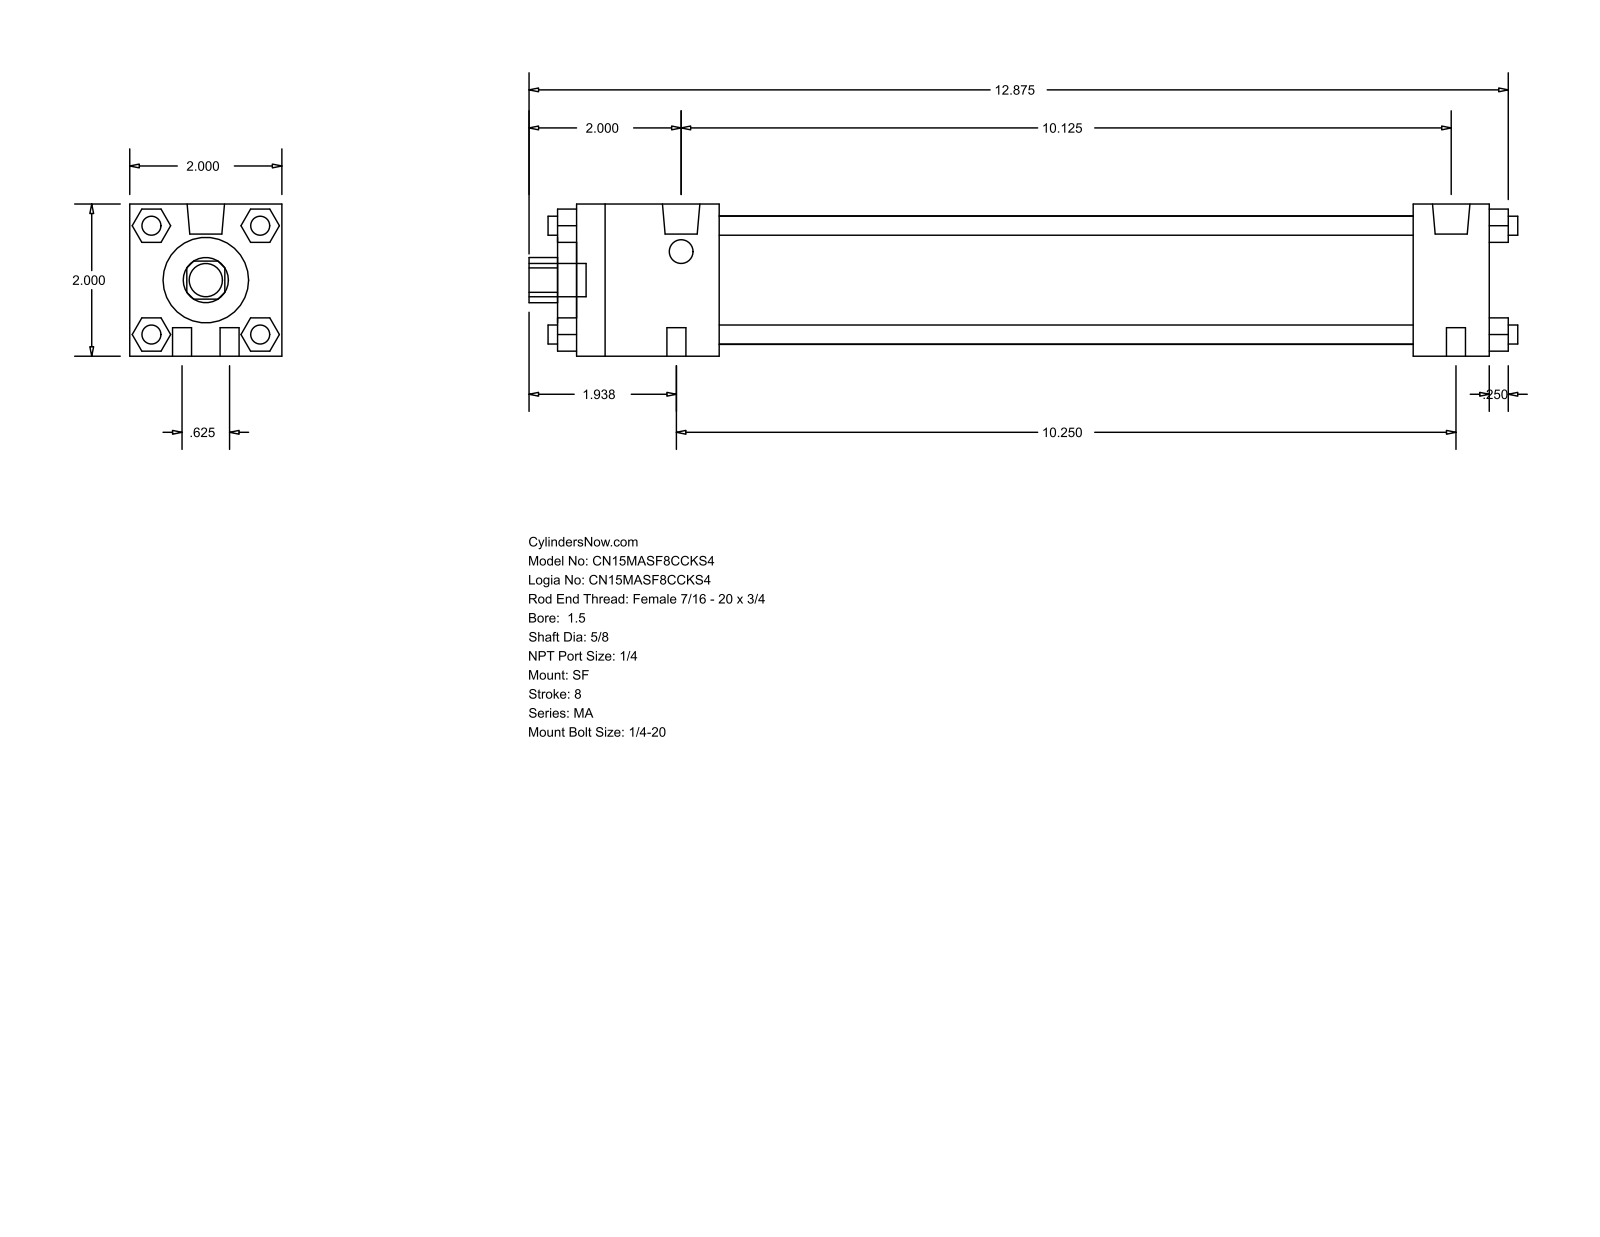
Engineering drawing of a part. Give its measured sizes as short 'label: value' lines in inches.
name: MA_SF__0150_0.625
written by: GSSL Pune (CONFIG_CONTROL_DESIGN)
unit: in
bodies: 0 solids, 124 faces (94 planar, 30 cylindrical, 0 other)
size: 13 × 2 × 2
holes: 1× ⌀0.625, 1× ⌀1.125, 1× ⌀1.69
bosses: 8× ⌀0.25, 2× ⌀0.492, 2× ⌀0.313, 1× ⌀0.437
rounds: 1× R0.297
face distances: 2, 12, 1.875, 11, 9.125, 10.125, 1, 0.25, 12.25, 2.125
